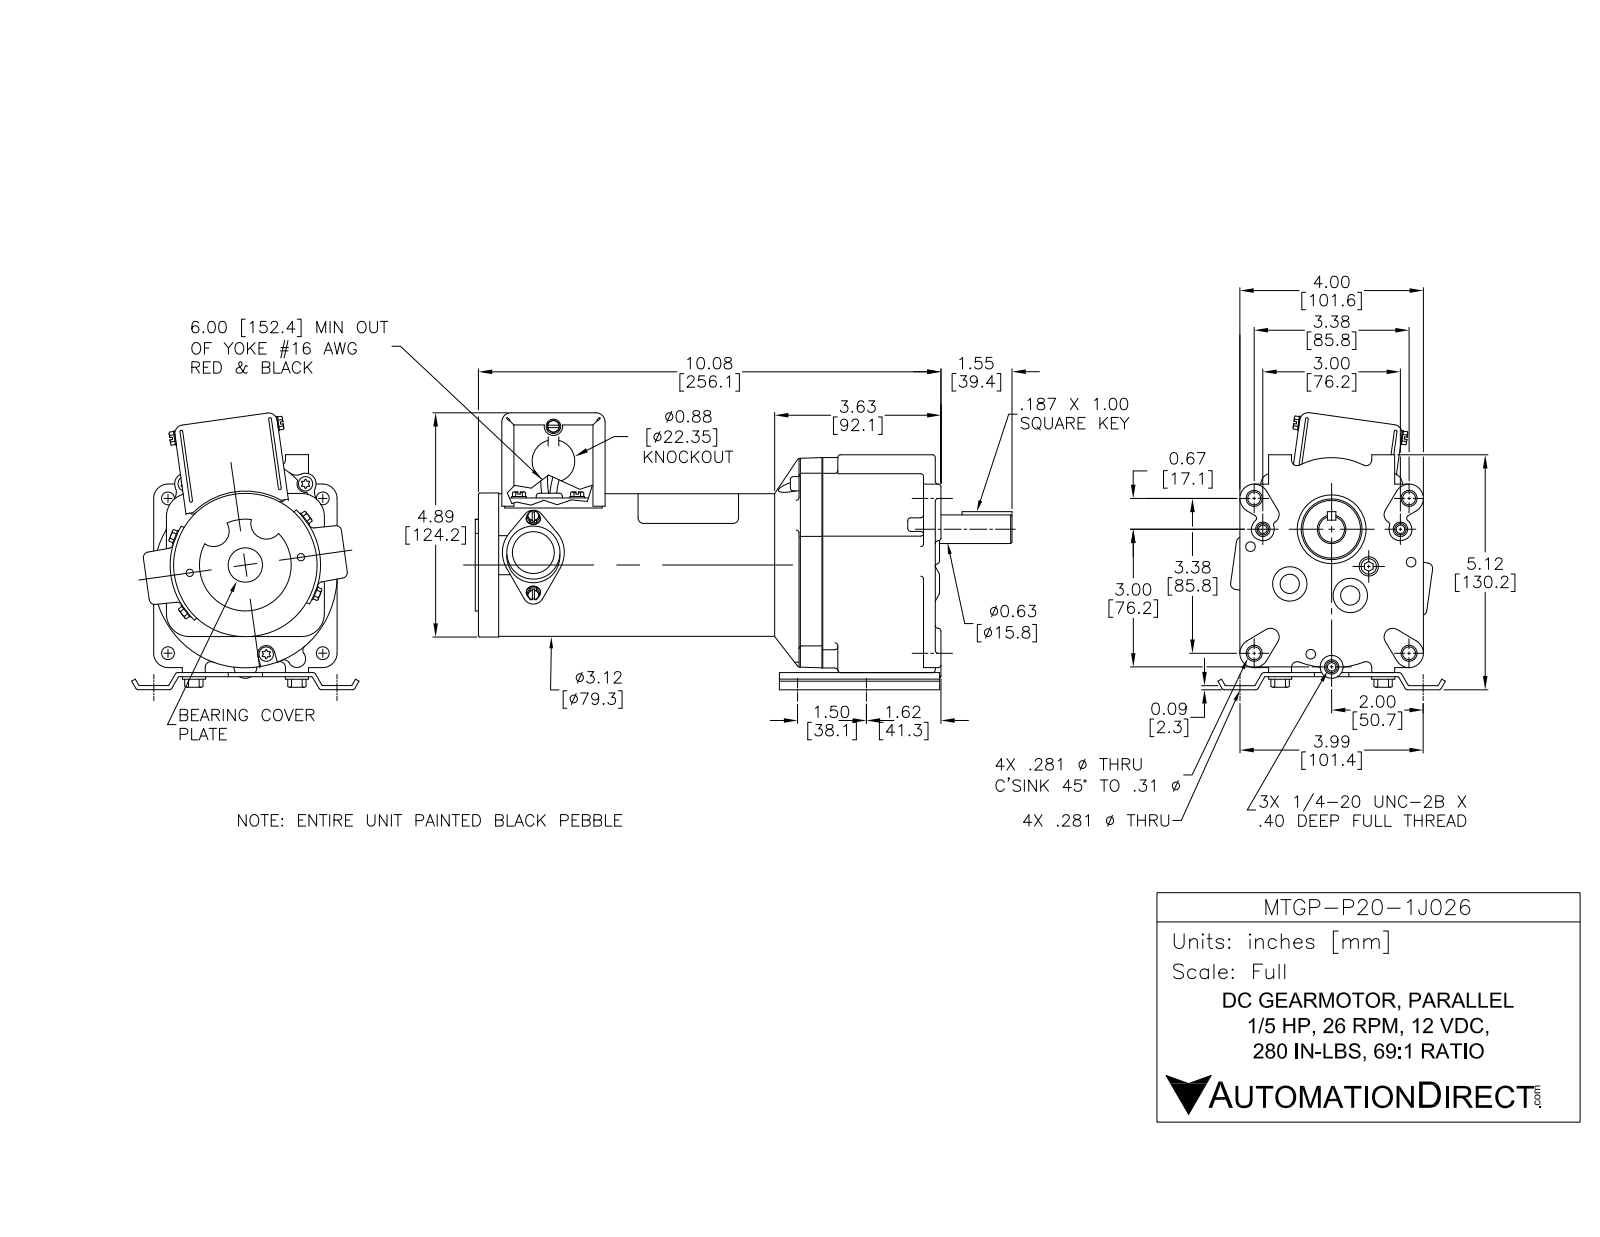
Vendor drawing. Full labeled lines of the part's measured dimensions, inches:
Part name (STEP PRODUCT): MTGP-P20-1J026
STEP written by: SolidWorks 2014 (AUTOMOTIVE_DESIGN)
Units: inches
Bodies: 53 solids, 984 faces (567 planar, 365 cylindrical, 52 other)
Overall size (bounding box): 11.698 × 6.209 × 4.939
Volume: 65.11 in³ · Surface area: 470.6 in²
Round holes (diameter × count): ⌀0.3 ×11, ⌀0.5 ×5, ⌀0.25 ×4, ⌀0.345 ×4, ⌀0.21 ×3, ⌀0.125 ×2, ⌀0.198 ×2, ⌀0.208 ×2, ⌀0.345 ×2, ⌀0.375 ×1, ⌀0.46 ×1, ⌀0.625 ×1
Round bosses / shafts (diameter × count): ⌀0.314 ×5, ⌀0.3 ×4, ⌀0.208 ×3, ⌀0.46 ×2, ⌀0.1 ×2, ⌀3.156 ×1, ⌀1.325 ×1, ⌀0.625 ×1
Partial cylindrical surfaces — rounded edges, fillets, slot ends (radius × count): R0.019 ×28, R0.1 ×23, R0.025 ×8, R0.25 ×7, R0.159 ×4, R0.19 ×4, R0.191 ×4, R0.234 ×4
Main face-to-face distances: 1.375, 3.495, 2.12, 0.09, 0.031, 0.25, 0.063, 0.05, 1.425, 3.545
Hole centre spacings: 1.62, 1.23, 1.5, 1.504, 1.603, 2.974, 3.375, 6.911
